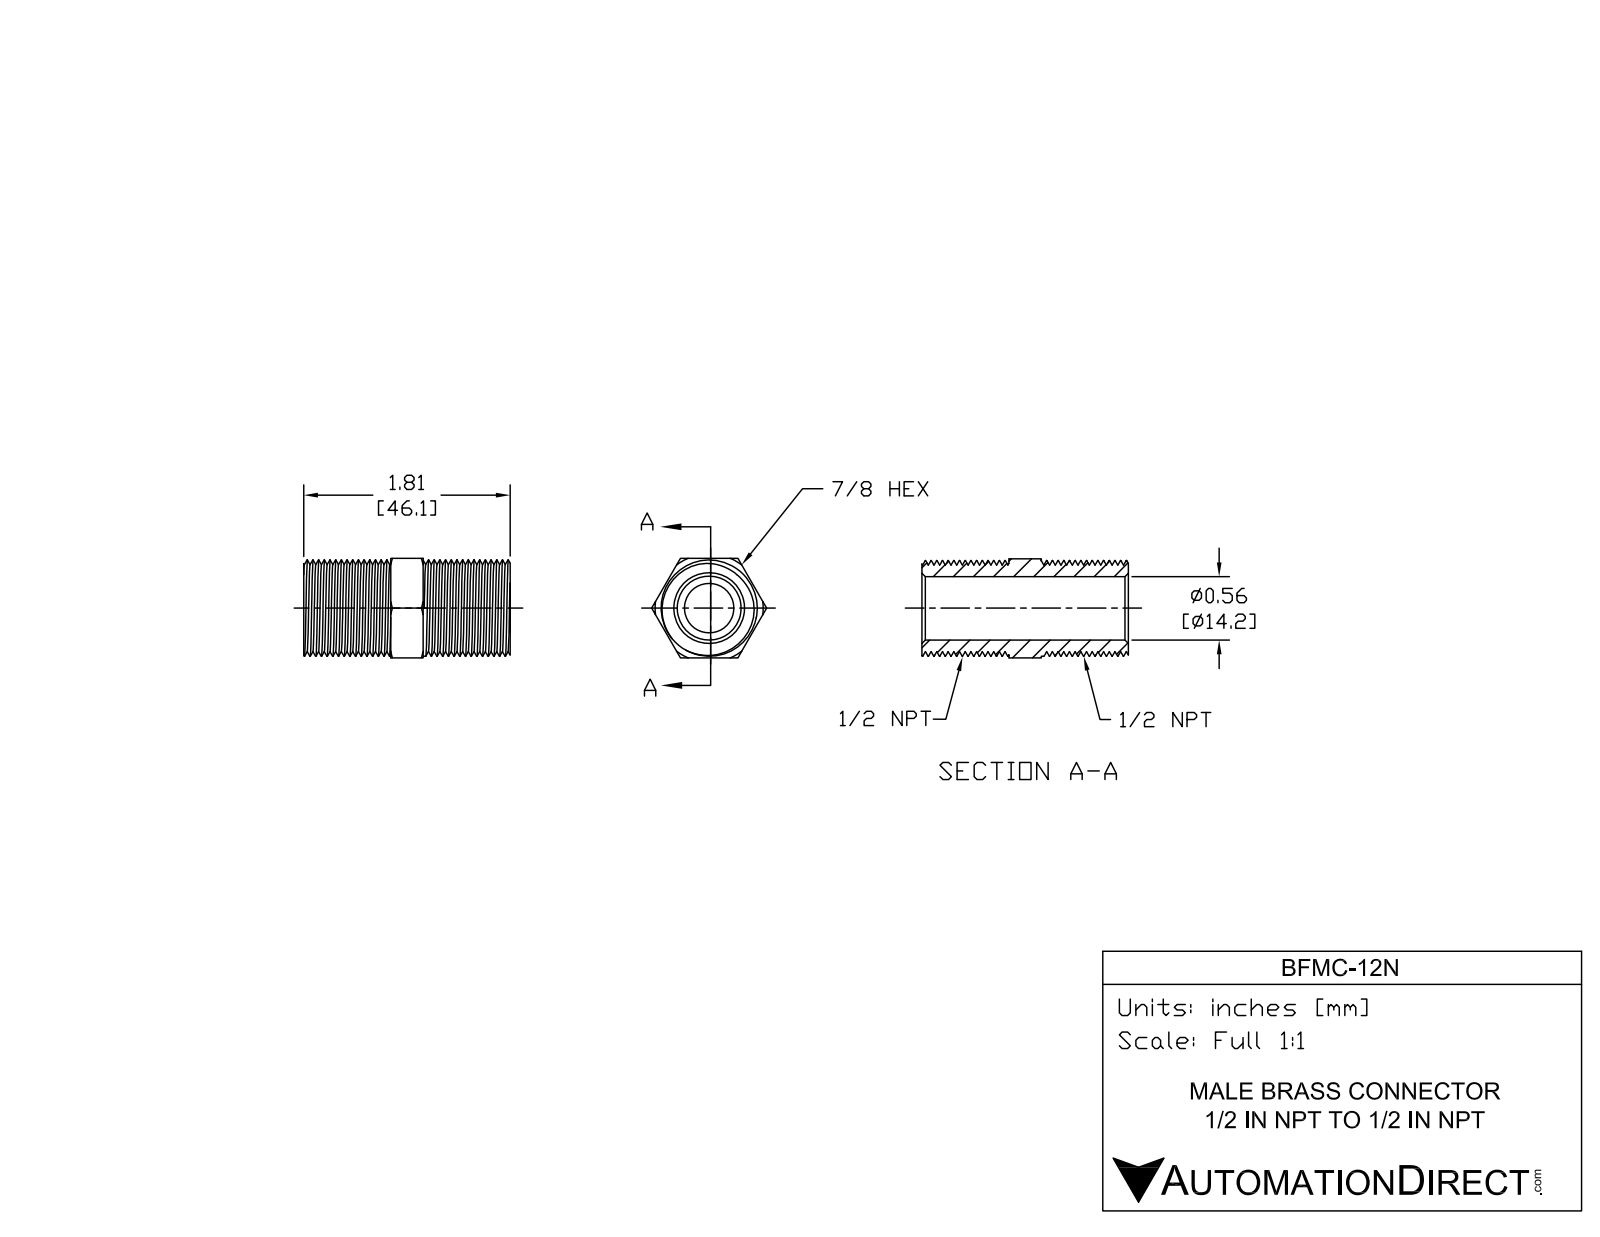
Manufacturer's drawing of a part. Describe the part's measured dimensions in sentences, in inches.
The part is named "BFMC-12N". Its 3-D file was written by "SolidWorks 2015 (CONFIG_CONTROL_DESIGN)". It is 1 solid with 101 faces: 12 planar, 65 cylindrical and 24 other. Overall it measures 1.814 by 1.01 by 0.875 inches. Its volume is 0.521 cubic inches and its surface area 12.35 square inches. Round holes: 1 of diameter 0.562. Round bosses or shafts: 1 of diameter 0.845. The main face-to-face distances are 0.875, 1.814, 0.765, 1.049, 0.284, 0.437.
